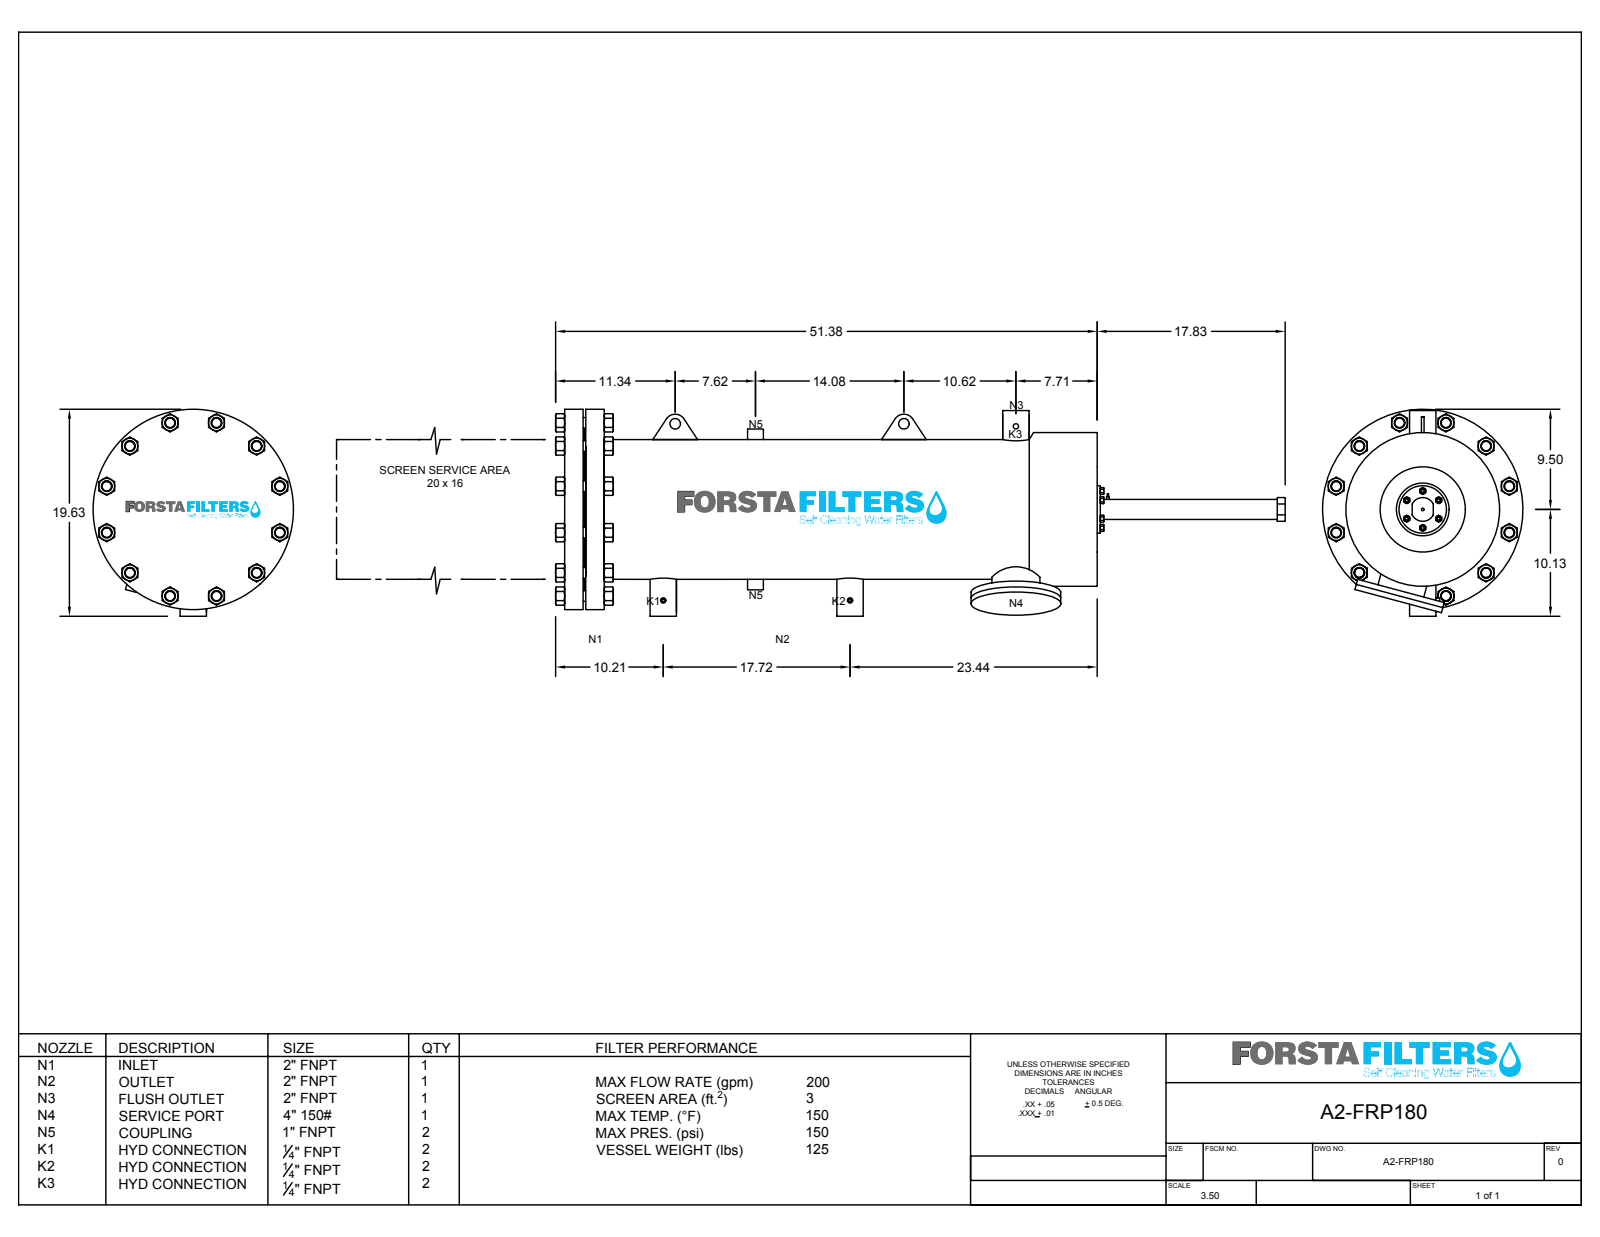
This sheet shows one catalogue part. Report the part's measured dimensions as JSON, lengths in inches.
{"part_name": "A2-FRP-180", "step_written_by": "SolidWorks 2018 (CONFIG_CONTROL_DESIGN)", "units": "inches", "bodies": {"solids": 31, "faces": 601, "planar": 302, "cylindrical": 293, "other": 6}, "overall_size": [66.233, 19, 19], "volume_in3": 1433, "surface_area_in2": 7196, "round_holes": [[0.75, 16], [1, 15], [0.25, 4], [0.375, 4], [0.375, 2], [2, 2], [4.106, 2], [1.51, 1], [1.996, 1], [12.858, 1], [14.187, 1]], "round_bosses_or_shafts": [[0.644, 3], [9, 2], [4.5, 2], [2.394, 2], [0.375, 2], [19, 1], [14.581, 1], [13.252, 1]], "partial_cylinders_radius": [[1, 2], [1.125, 1]], "face_to_face_distances": [1.75, 2, 0.25, 0.5, 48.62, 46.87, 46.62, 3.75, 44.87, 48.423], "hole_center_spacings": [2.87, 3.75, 5.303, 6.929, 8.5, 12.02, 16.42, 9.815]}
